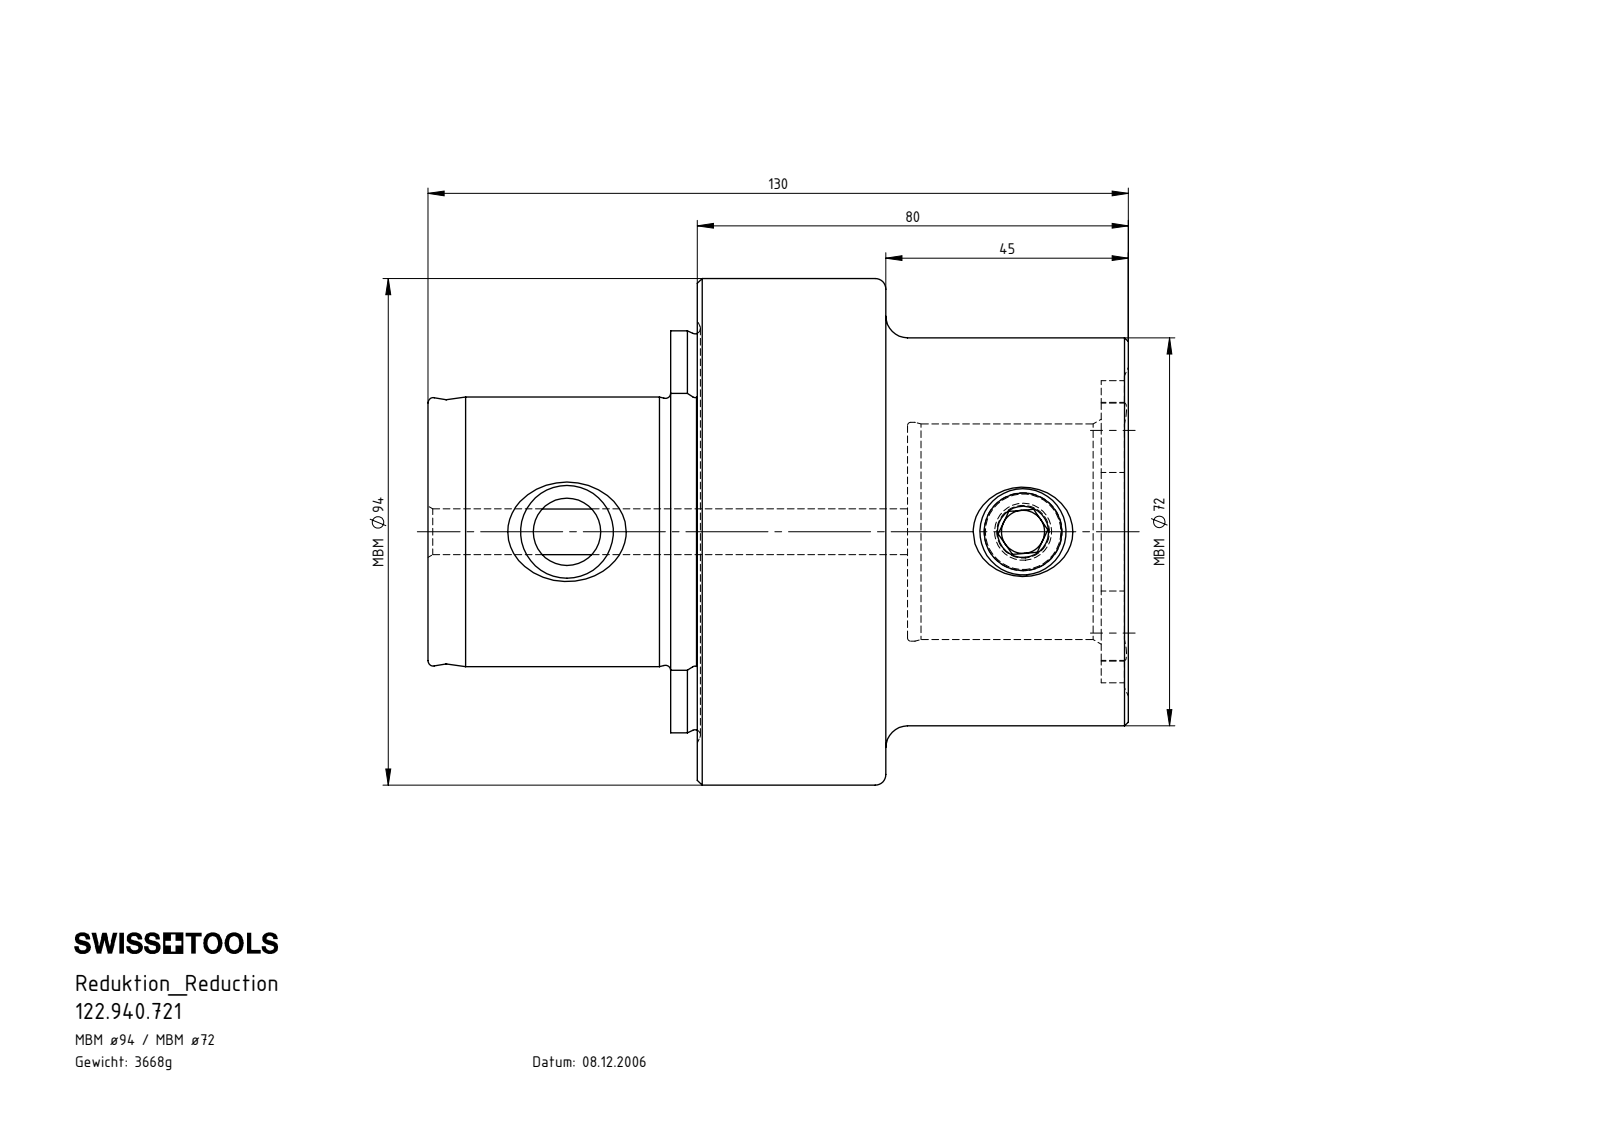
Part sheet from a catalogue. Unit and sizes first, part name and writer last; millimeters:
Units: millimetres
Overall size (bounding box): 130 × 94 × 94
Round holes (diameter × count): ⌀8 ×1, ⌀8.5 ×1, ⌀12.5 ×1, ⌀14.5 ×1, ⌀40 ×1, ⌀40.6 ×1
Round bosses / shafts (diameter × count): ⌀94 ×1, ⌀72 ×1, ⌀50 ×1, ⌀16 ×1
Partial cylindrical surfaces — rounded edges, fillets, slot ends (radius × count): R5.2 ×4, R23.75 ×1, R28.02 ×1, R37.27 ×1
Main face-to-face distances: 39.95, 50, 45.05, 4.95, 85, 35, 89, 43.95, 39, 4
Hole centre spacings: 84.65
Volume: 467 233 mm³ · Surface area: 51 743 mm²
Bodies: 2 solids, 135 faces (35 planar, 35 cylindrical, 65 other)
Part name (STEP PRODUCT): 122.940.721; MB7-ER1.001.022_A; MB9-MB7.K01.080_C
STEP written by: SolidWorks 2017 (AUTOMOTIVE_DESIGN)
